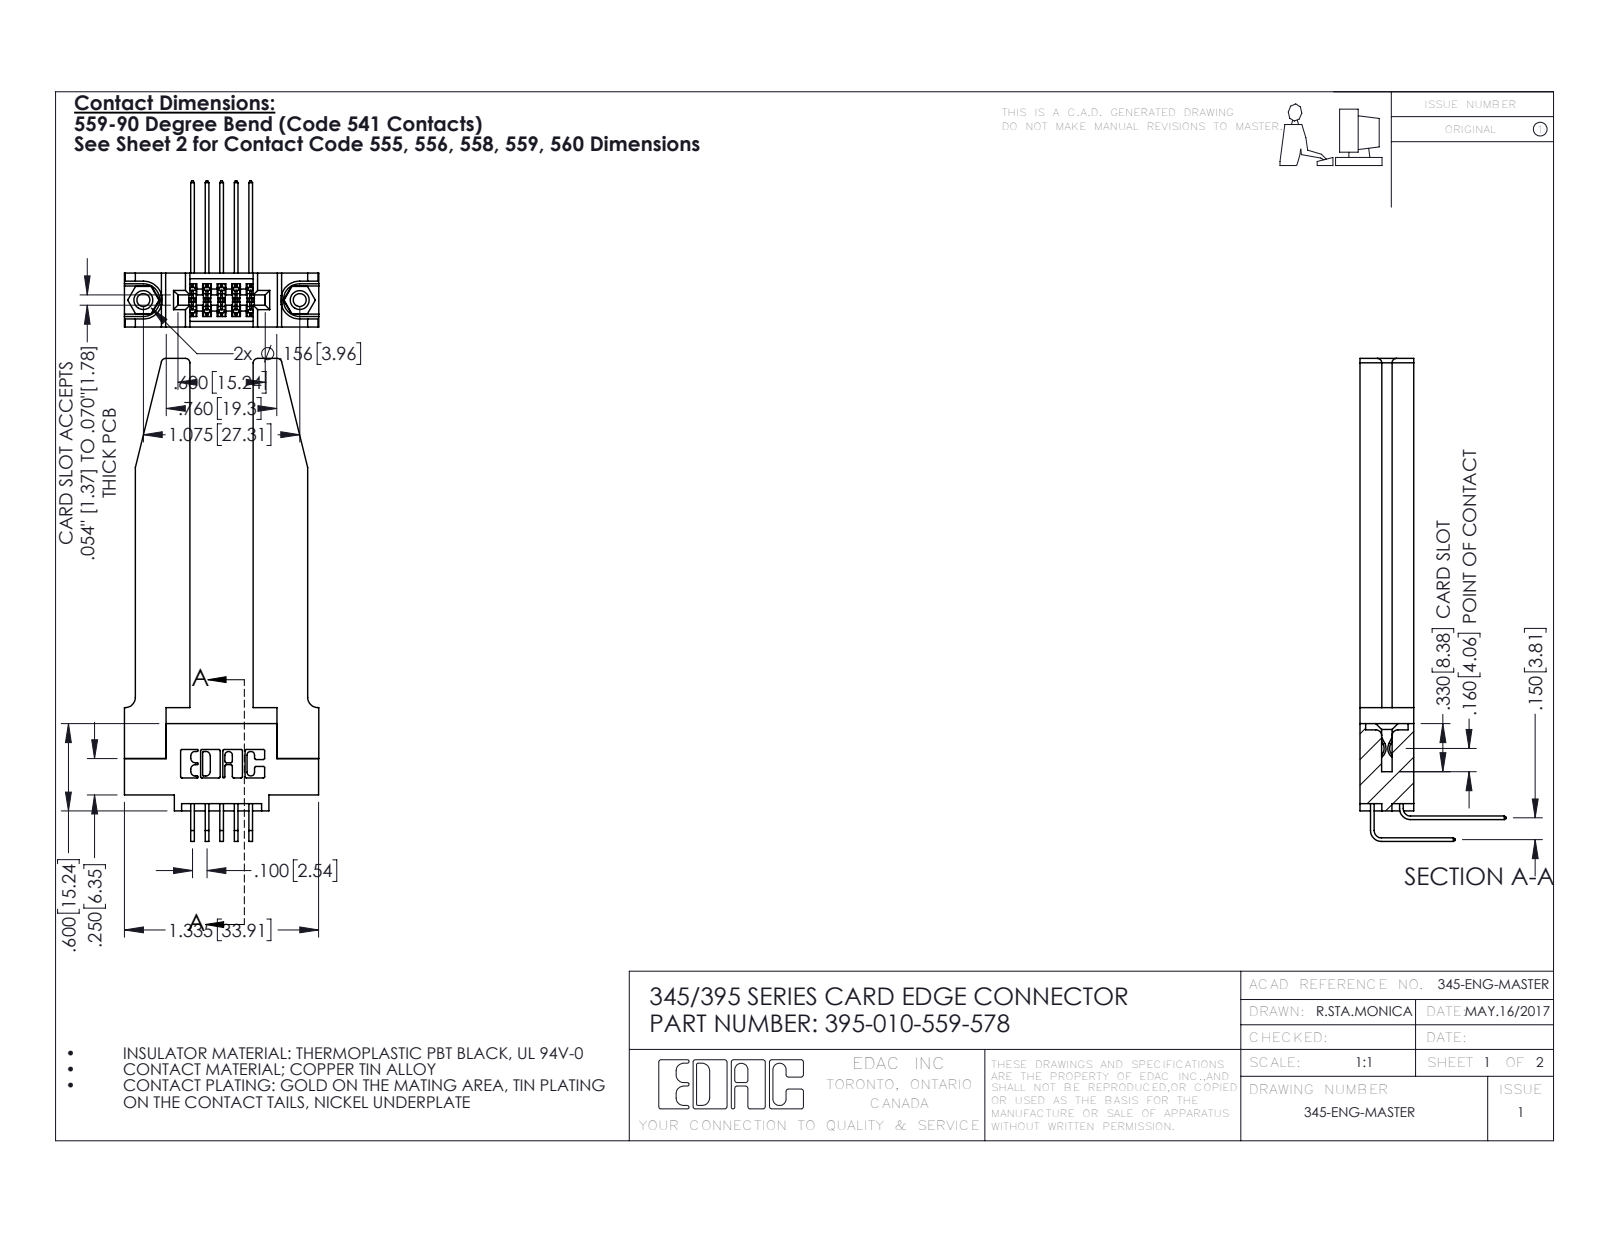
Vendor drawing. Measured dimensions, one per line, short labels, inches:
name: 395-010-559-578; 345 Part_0.110 Offset - 0.156 Dia-TH; 345-220-078_345-220-078; 345-250-001_345-250-001-102 (+2 more)
written by: SolidWorks 2016 (CONFIG_CONTROL_DESIGN)
unit: in
bodies: 15 solids, 884 faces (576 planar, 256 cylindrical, 52 other)
size: 3.319 × 1.336 × 1.005
volume: 0.653 in³; area: 16.78 in²
holes: 2× ⌀0.089, 2× ⌀0.125, 2× ⌀0.156, 1× ⌀0.064
bosses: 2× ⌀0.155
rounds: 22× R0.01, 16× R0.006, 8× R0.03, 6× R0.007, 6× R0.031, 3× R0.026, 2× R0.014, 2× R0.019
face distances: 0.37, 0.15, 0.22, 0.435, 0.148, 0.072, 0.298, 0.077, 0.071, 0.2
hole spacings: 0.27, 0.847, 1.075
